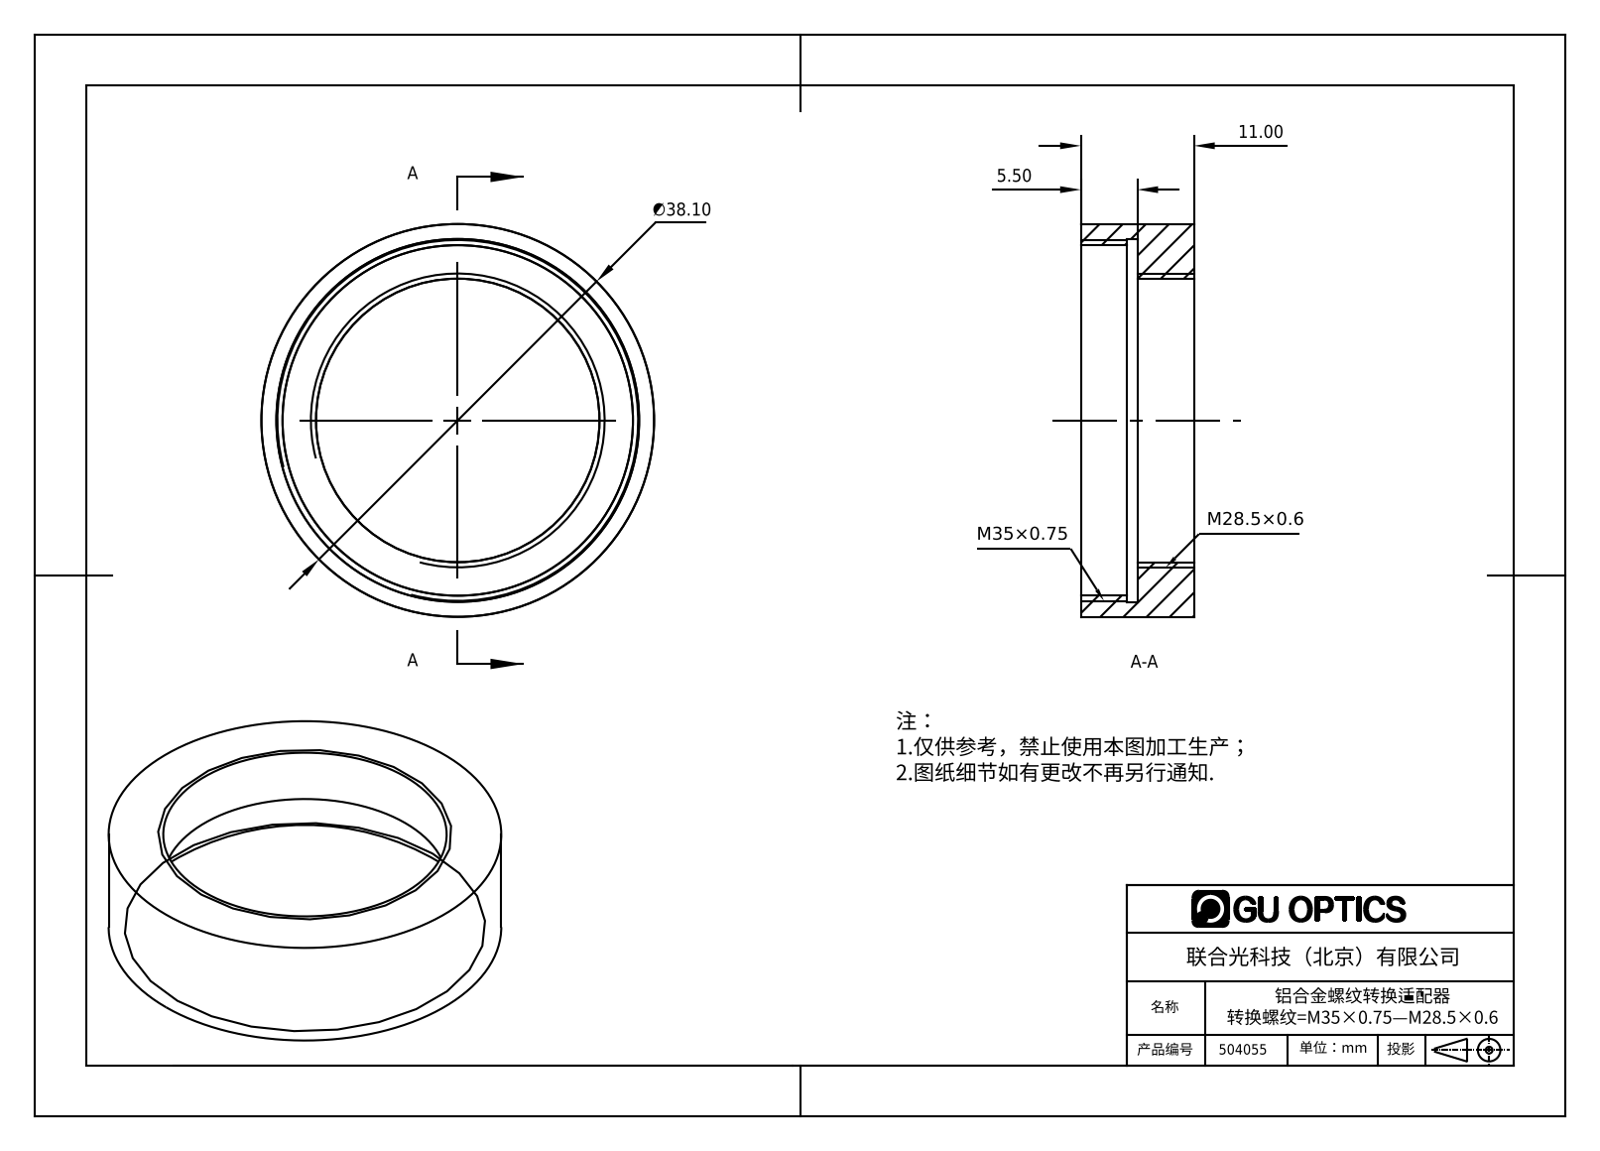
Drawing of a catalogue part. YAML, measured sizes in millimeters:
part_name: "504055"
step_written_by: "SolidWorks 2016 (AUTOMOTIVE_DESIGN)"
units: millimeters
bodies: {solids: 1, faces: 12, planar: 4, cylindrical: 8, other: 0}
overall_size: [38.1, 38.1, 11]
volume: 4215
surface_area: 3606
round_holes:
  - {diameter: 27.5, count: 1}
  - {diameter: 34, count: 1}
  - {diameter: 35.2, count: 1}
round_bosses_or_shafts:
  - {diameter: 38.1, count: 1}
face_to_face_distances: [5.5, 11, 4.5, 1, 6.5]
